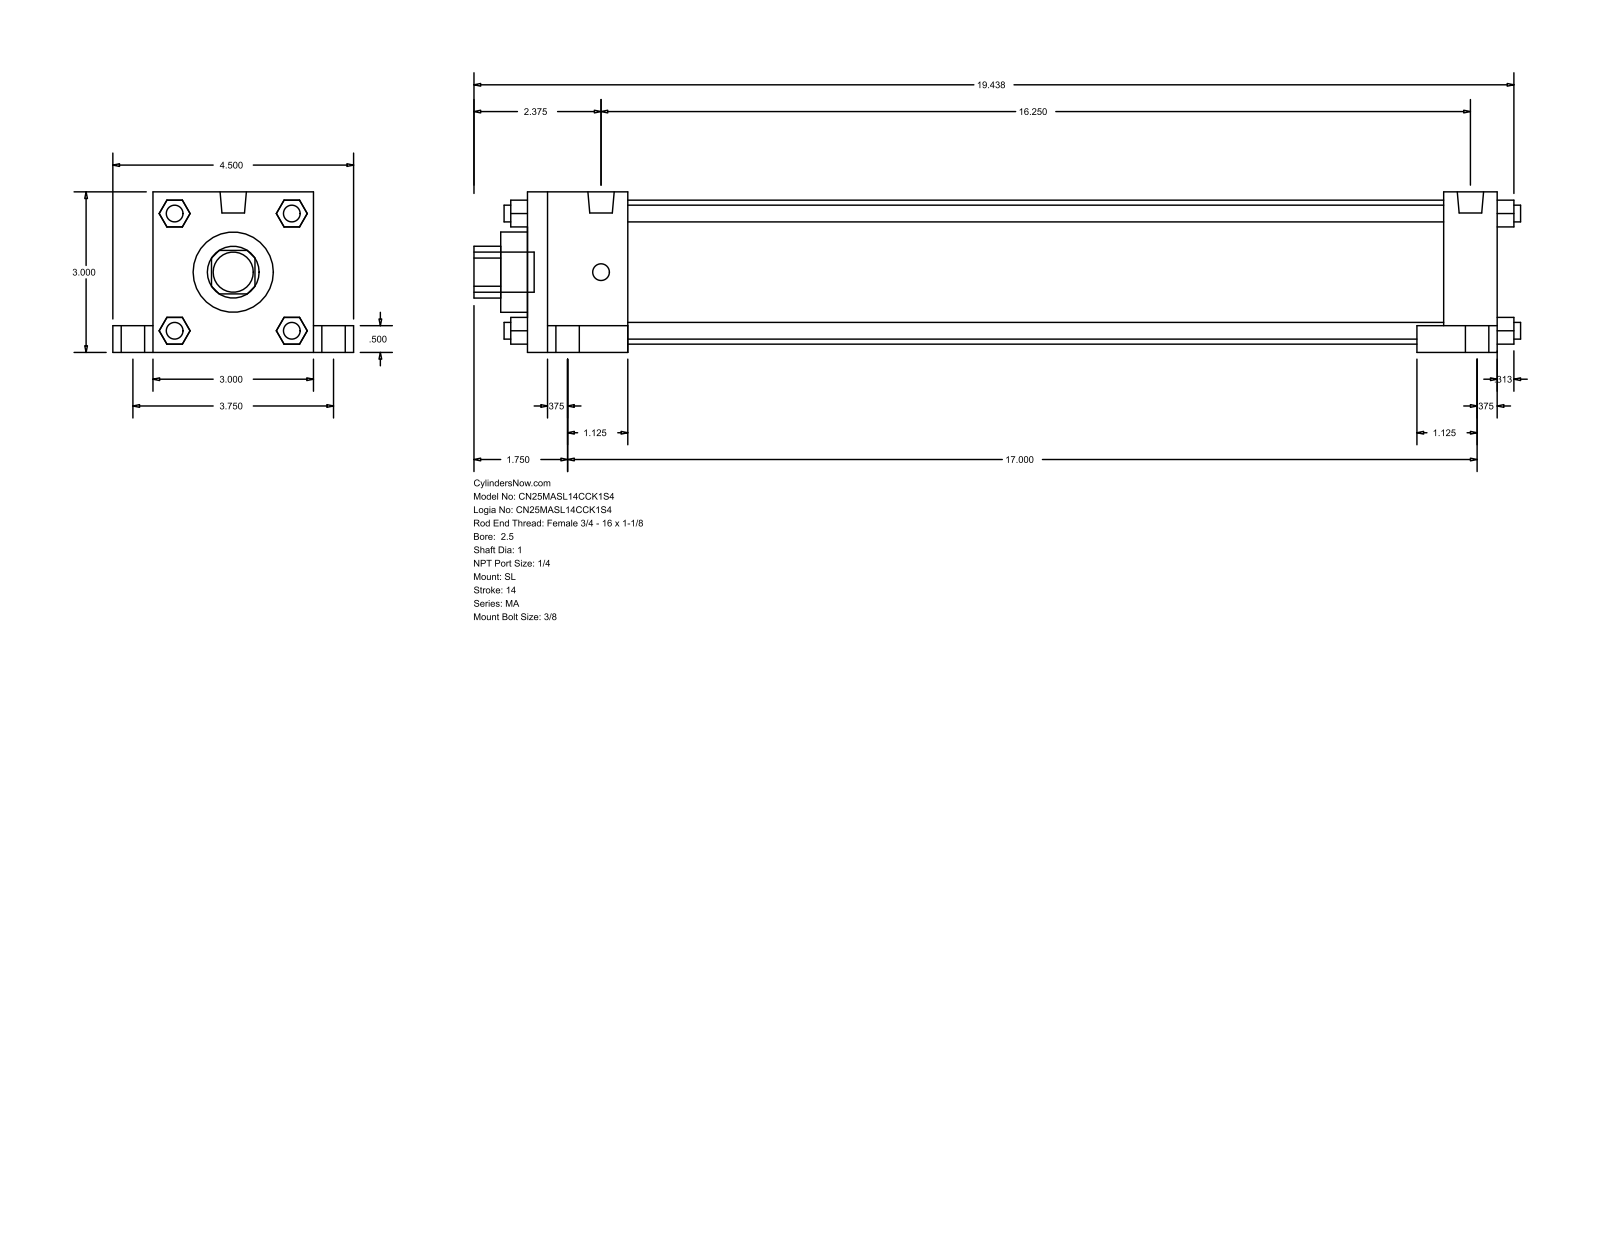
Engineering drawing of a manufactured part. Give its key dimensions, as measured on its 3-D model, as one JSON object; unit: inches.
{"part_name": "MA_SL__0250_1", "step_written_by": "GSSL Pune (CONFIG_CONTROL_DESIGN)", "units": "inches", "bodies": {"solids": 0, "faces": 148, "planar": 112, "cylindrical": 36, "other": 0}, "overall_size": [19.563, 4.5, 3], "round_holes": [[1, 1], [1.5, 1], [2.69, 1]], "round_bosses_or_shafts": [[0.313, 8], [0.687, 4], [0.437, 4], [0.492, 2], [0.75, 1]], "partial_cylinders_radius": [[0.484, 1]], "face_to_face_distances": [3, 18.125, 0.5, 15.25, 1, 1.875, 16.25, 17.125, 0.75, 3.75]}
